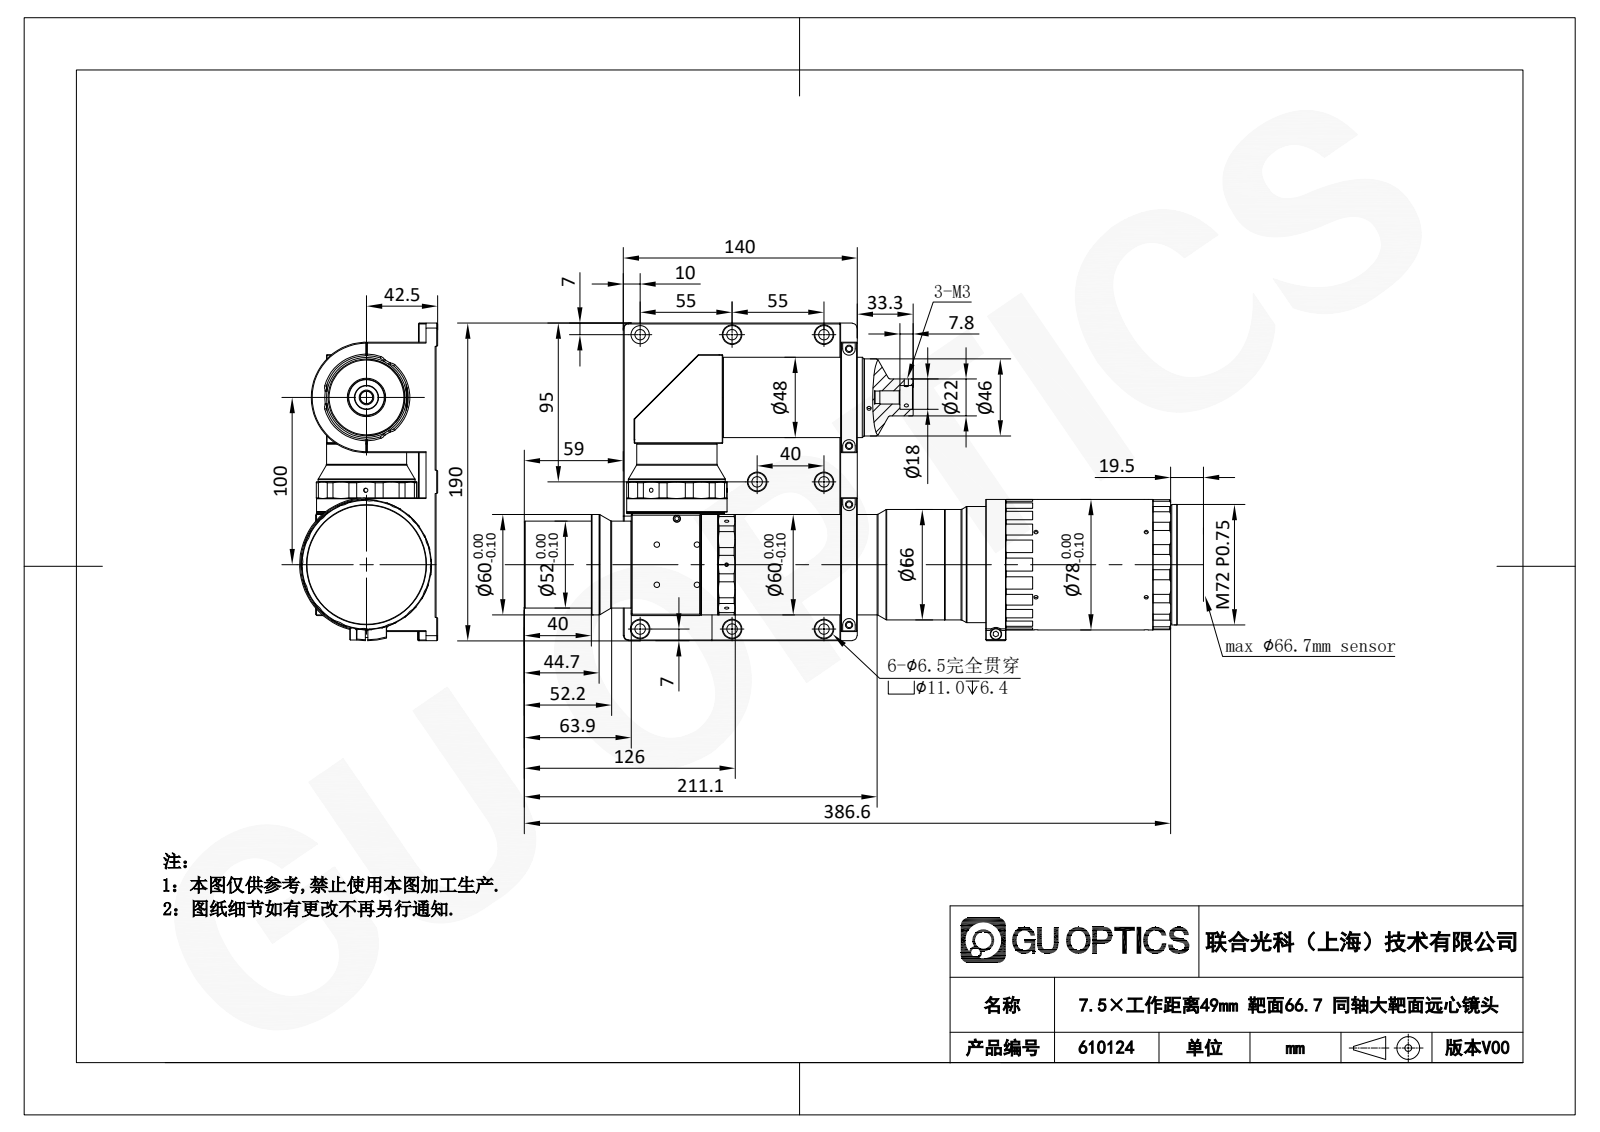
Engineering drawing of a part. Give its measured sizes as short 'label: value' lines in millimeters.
name: DTCA150M-8.9C-G-M72-19.5-AL(8)
written by: SolidWorks 2017 (CONFIG_CONTROL_DESIGN)
unit: mm
bodies: 1 solid, 1343 faces (408 planar, 500 cylindrical, 435 other)
size: 390.57 × 190 × 82.53
volume: 2 063 000 mm³; area: 213 946 mm²
holes: 18× ⌀2.5, 16× ⌀3.3, 16× ⌀4.5, 12× ⌀7.5, 8× ⌀6.5, 8× ⌀11, 6× ⌀2.4, 4× ⌀6, 2× ⌀1.5, 2× ⌀2.2, 2× ⌀4, 2× ⌀56.1
bosses: 2× ⌀60, 2× ⌀56, 2× ⌀48, 1× ⌀78, 1× ⌀74, 1× ⌀72, 1× ⌀70.8, 1× ⌀69.5
rounds: 38× R15, 12× R2, 10× R3, 6× R5, 5× R1.5, 4× R0.5, 4× R3.75, 2× R1
face distances: 10.5, 1, 11.5, 191.35, 10, 201.35, 72, 6.5, 61.5, 61
hole spacings: 24, 40, 66, 5, 6, 16.97, 33.94, 41.4
